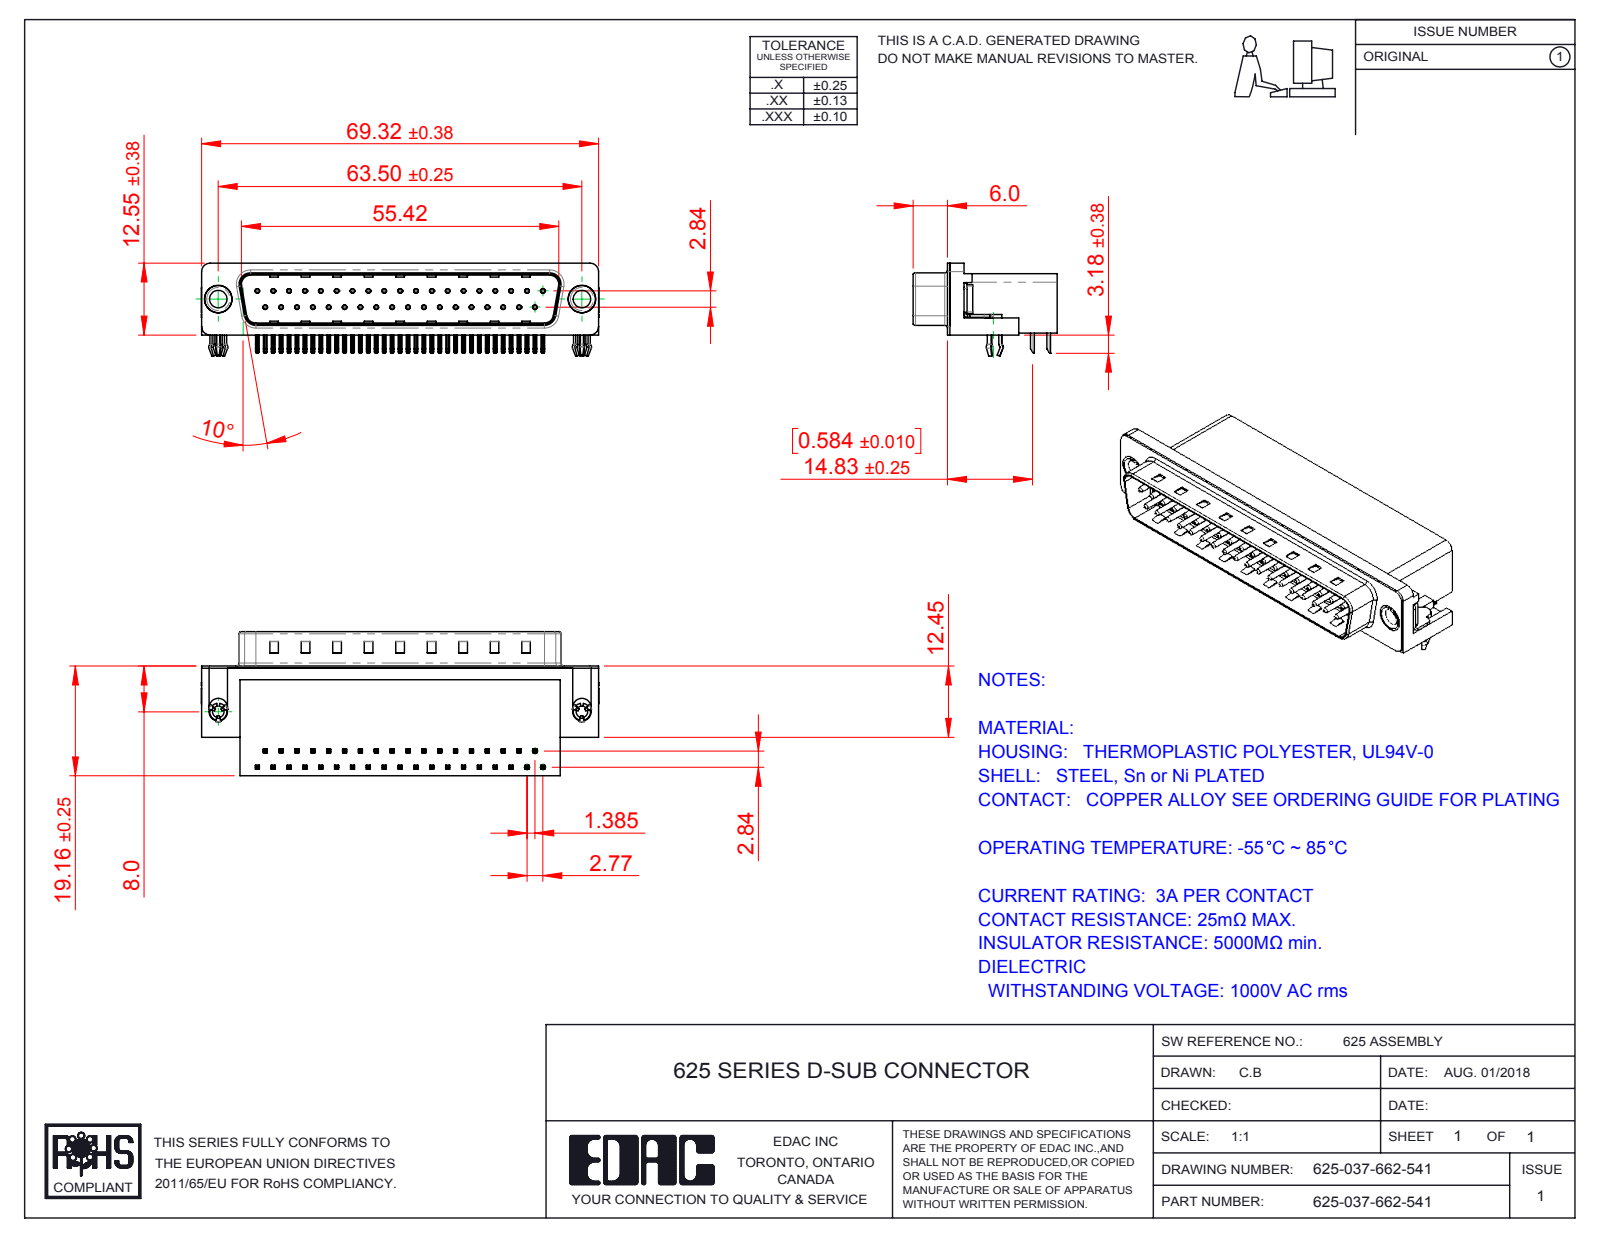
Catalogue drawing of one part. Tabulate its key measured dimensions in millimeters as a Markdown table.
| quantity | value |
| --- | --- |
| part name | 625 Housing_37 Socket; 625 Contact Top; 625 Thru Hole Rivet; 625 3 Prong Board Lock (+3 more) |
| STEP written by | SolidWorks 2016 (CONFIG_CONTROL_DESIGN) |
| units | millimeters |
| bodies | 43 solids, 3265 faces (2051 planar, 905 cylindrical, 309 other) |
| overall size | 69.4 × 25.16 × 16.25 |
| volume | 12 597 mm³ |
| surface area | 11 792 mm² |
| round holes (diameter × count) | 0.35 × 37, 0.8 × 37, 2 × 2, 3.05 × 2, 4 × 2, 4.8 × 2, 5 × 2 |
| round bosses / shafts (diameter × count) | 0.75 × 37, 4.9 × 2, 4.75 × 2, 3.85 × 2, 3 × 2 |
| partial cylindrical surfaces (radius × count) | 0.25 × 160, 0.12 × 74, 1 × 16, 0.5 × 9, 1.6 × 8, 1.5 × 7, 0.9 × 4, 2 × 4 |
| main face-to-face distances | 10.34, 0.4, 18.76, 8.76, 19.16, 2.84, 2.09, 10.1, 1.74, 8.36 |
| hole center spacings | 3.16, 2.77, 5.54, 8.31, 11.08, 13.85, 19.39, 22.16 |
